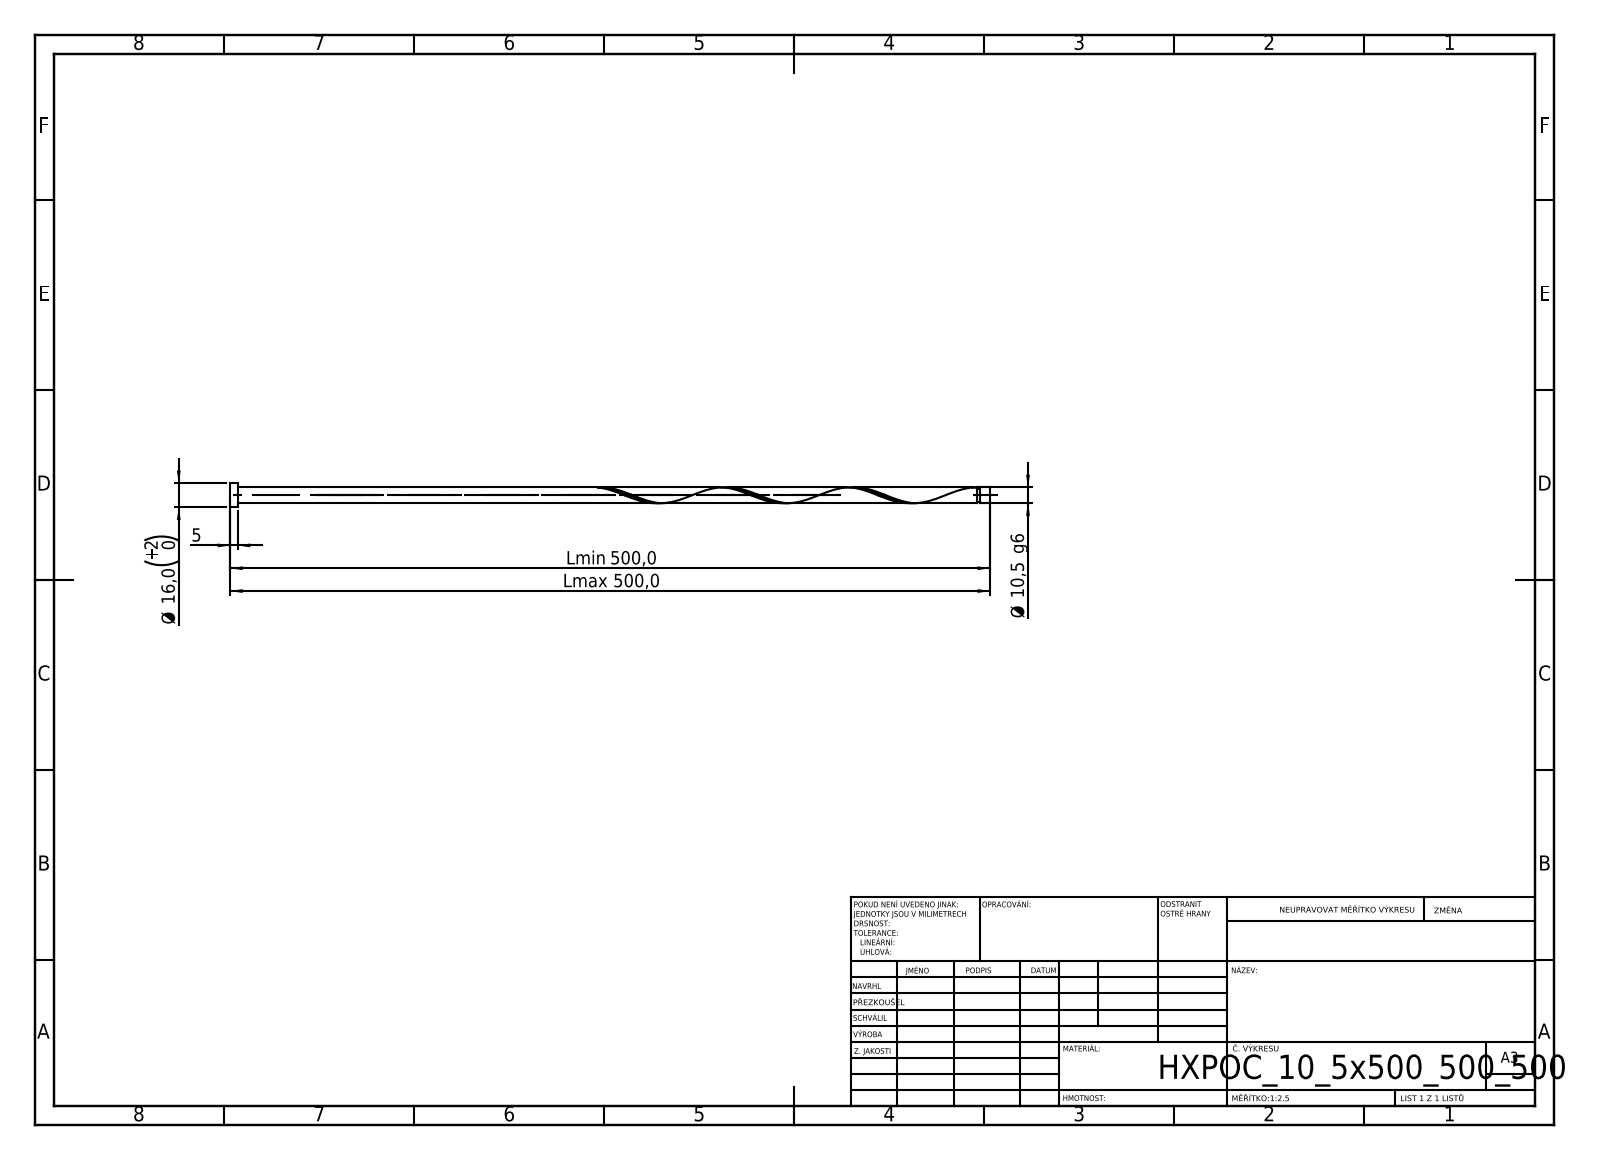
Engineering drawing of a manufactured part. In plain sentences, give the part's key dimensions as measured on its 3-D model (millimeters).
Its 3-D file was written by "SolidWorks 2019 (CONFIG_CONTROL_DESIGN)". It is 1 solid with 21 faces: 6 planar, 14 cylindrical and 1 other. Overall it measures 500 by 16 by 16 millimeters. Its volume is 43 387 cubic millimeters and its surface area 17 304 square millimeters. Round bosses or shafts: 1 of diameter 16, 1 of diameter 10.5, 1 of diameter 8.4. The main face-to-face distances are 5, 500, 495, 493.48, 488.48, 6.52, 491.38, 486.38, 2.1, 8.62.
